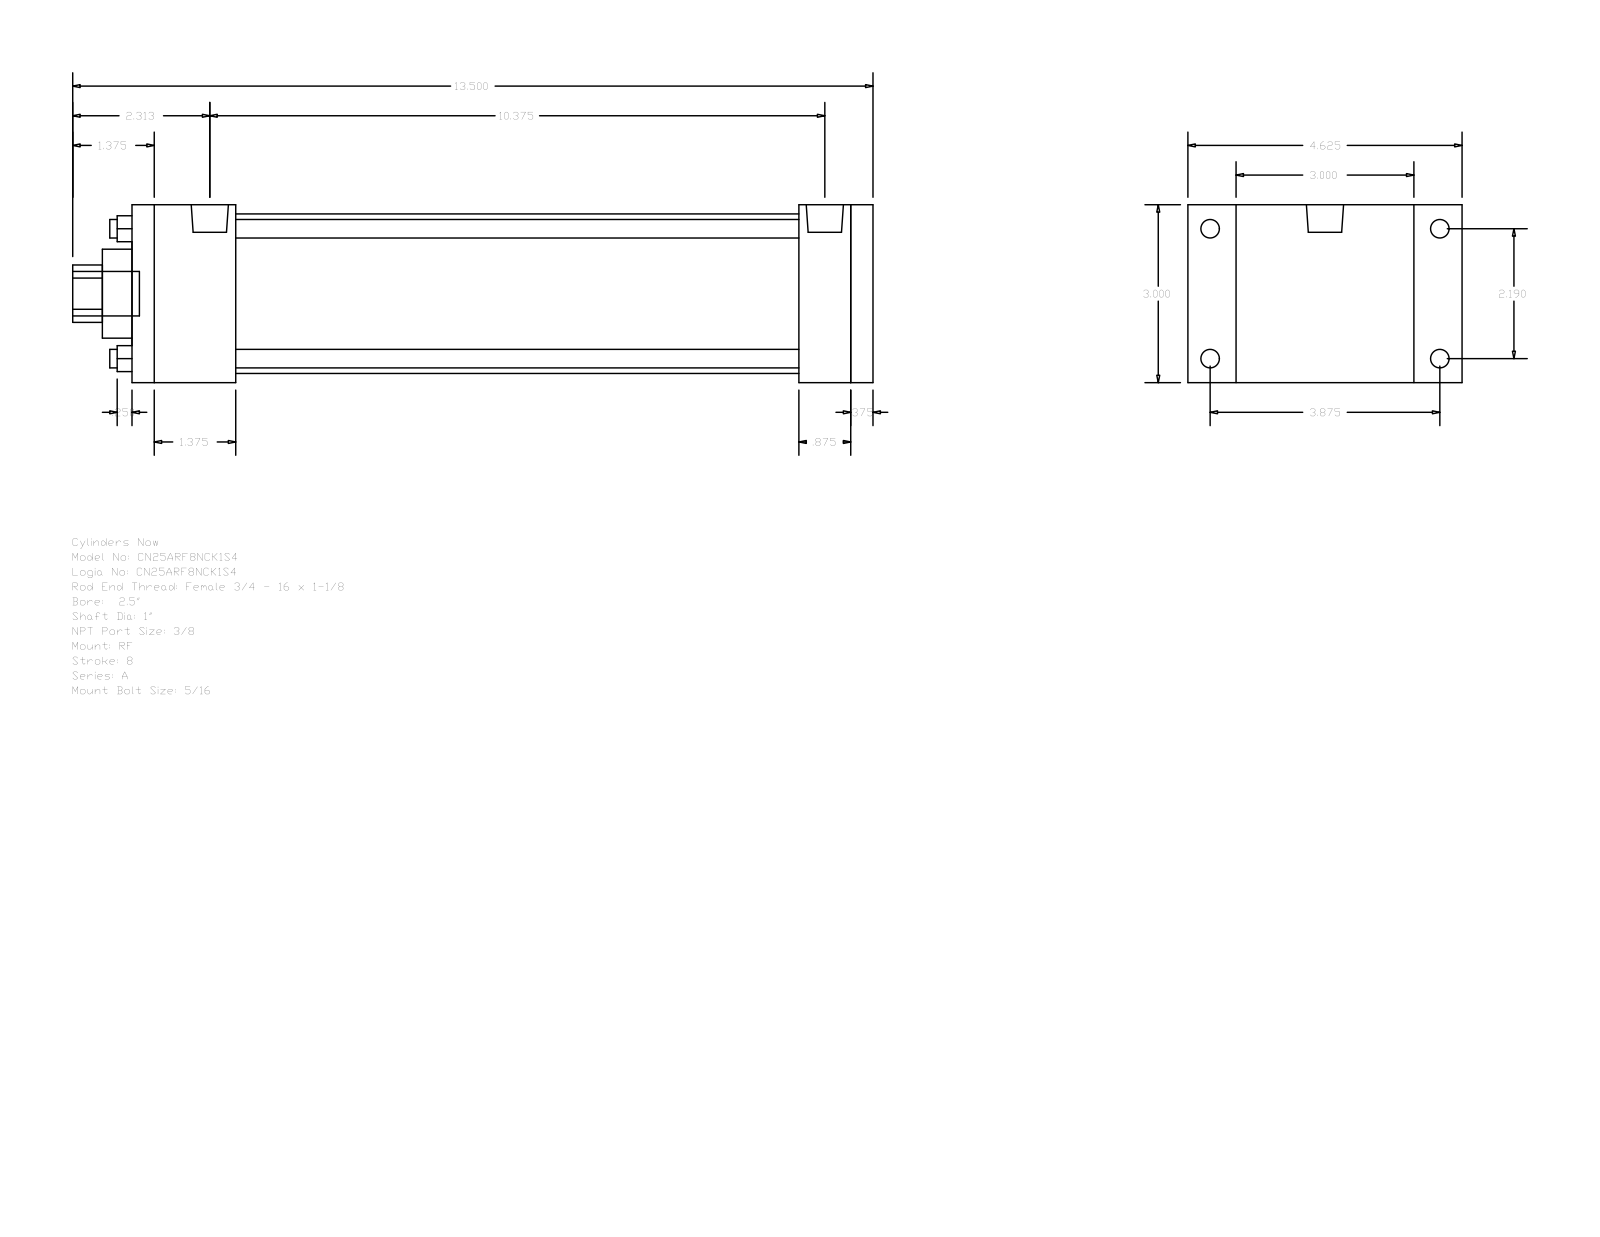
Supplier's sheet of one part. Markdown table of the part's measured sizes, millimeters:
| quantity | value |
| --- | --- |
| part name | A_RF__0250_1 |
| STEP written by | GSSL Pune (CONFIG_CONTROL_DESIGN) |
| units | millimeters |
| bodies | 0 solids, 92 faces (64 planar, 28 cylindrical, 0 other) |
| overall size | 342.9 × 117.47 × 76.2 |
| round holes (diameter × count) | 7.94 × 4, 25.4 × 1, 38.1 × 1, 68.33 × 1 |
| round bosses / shafts (diameter × count) | 7.94 × 4, 5.56 × 4, 15.93 × 2, 19.05 × 1 |
| partial cylindrical surfaces (radius × count) | 12.29 × 1 |
| main face-to-face distances | 76.2, 317.5, 9.52, 307.98, 44.45, 285.75, 241.3, 263.53, 273.05, 22.23 |
| hole center spacings | 39.33, 55.62, 78.66 |
